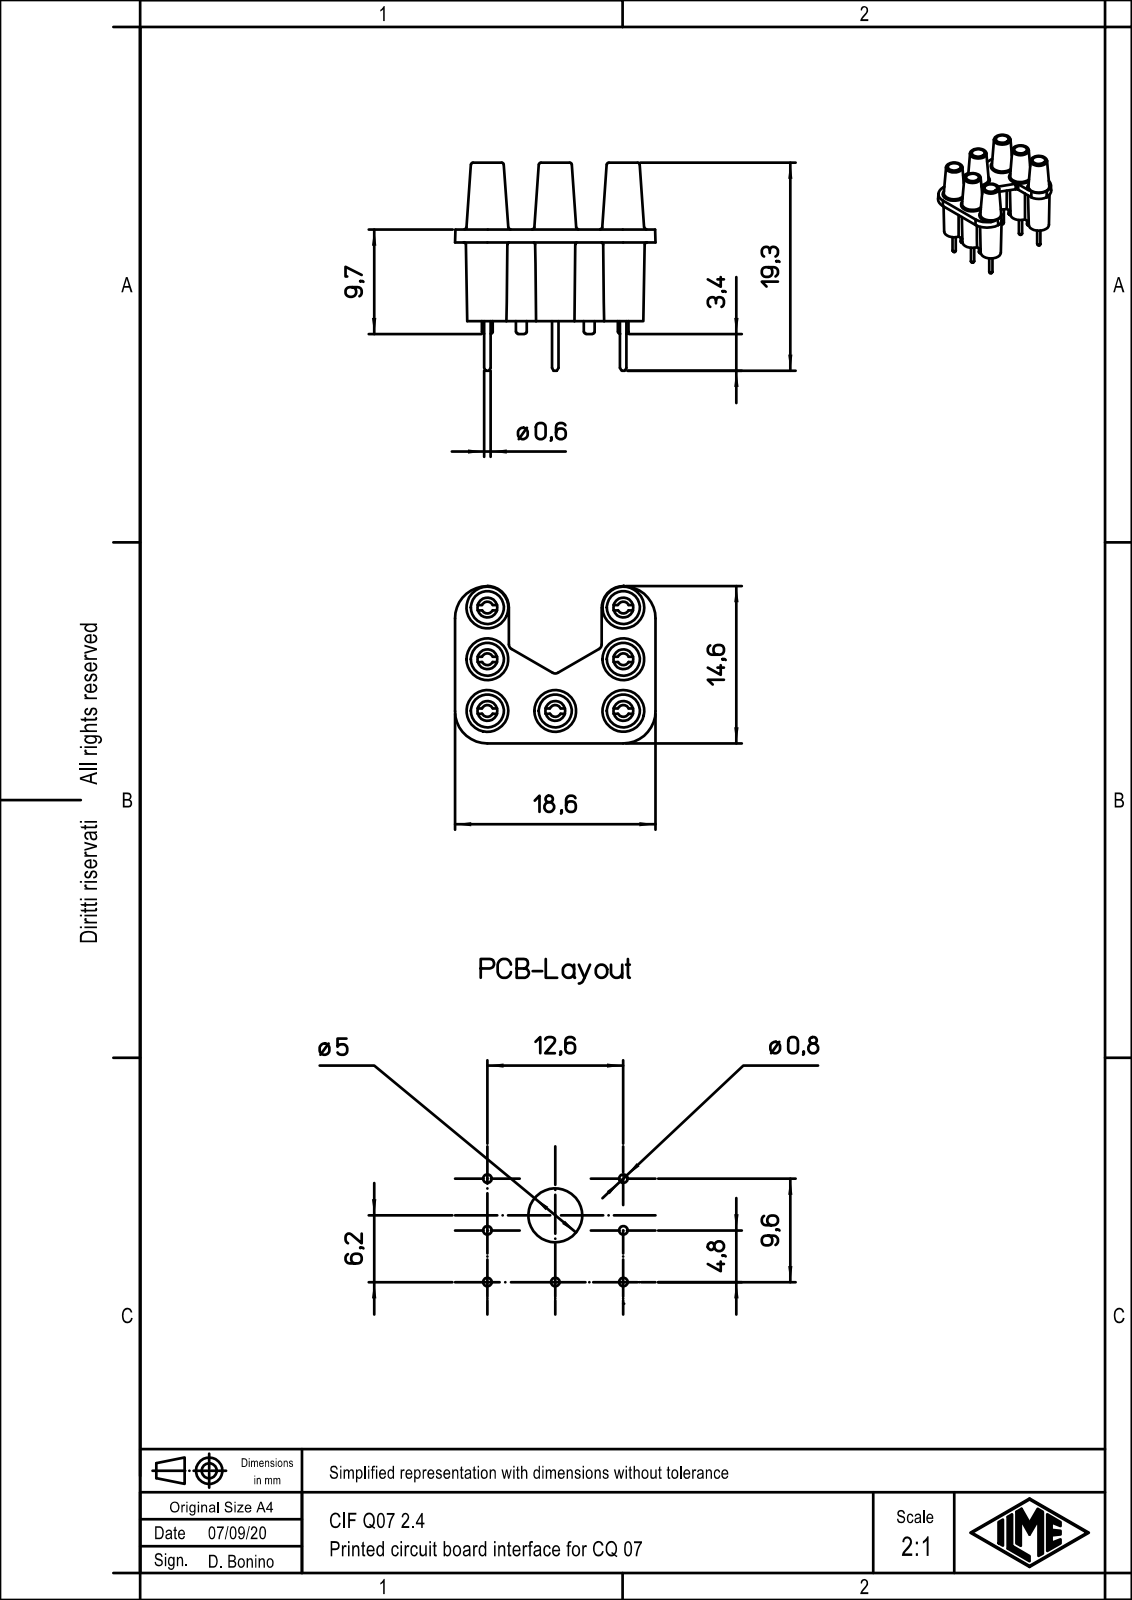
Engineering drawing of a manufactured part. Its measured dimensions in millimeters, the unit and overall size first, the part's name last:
Units: millimetres
Overall size (bounding box): 19.3 × 18.6 × 14.6
Round holes (diameter × count): ⌀2 ×7
Round bosses / shafts (diameter × count): ⌀4 ×7, ⌀0.6 ×7, ⌀1 ×6
Partial cylindrical surfaces — rounded edges, fillets, slot ends (radius × count): R0.55 ×7, R3 ×4, R0.5 ×3
Main face-to-face distances: 1.2, 8.5, 7.3, 0.5, 4.8, 2.4, 3.6, 0.35, 0.85, 12.6
Hole centre spacings: 4.8, 13.48, 12.6, 6.3, 7.92, 9.6, 11.48, 15.84
Volume: 1 310 mm³ · Surface area: 1 936 mm²
Bodies: 1 solid, 219 faces (92 planar, 73 cylindrical, 54 other)
Part name (STEP PRODUCT): CIF_Q07_2.4
STEP written by: Creo Elements/Direct Modeling 20.1B 02-Apr-2019 (C) Parametric Technology GmbH (AUTOMOTIVE_DESIGN)
